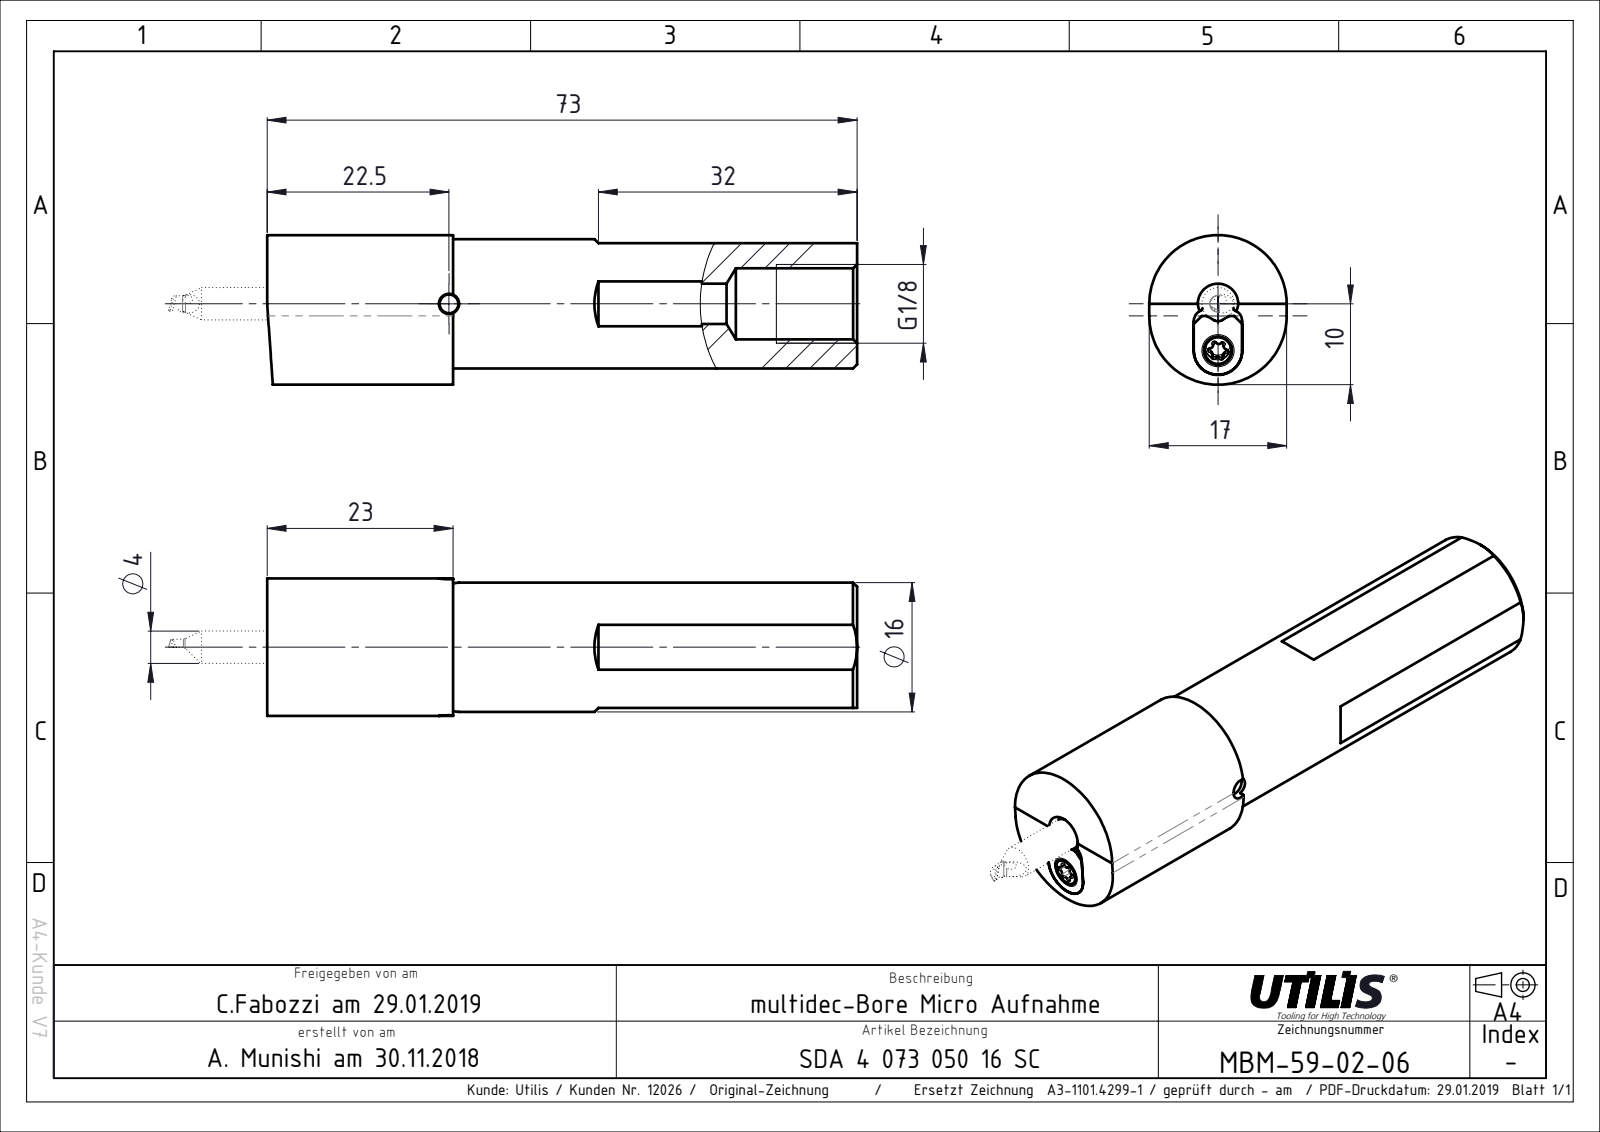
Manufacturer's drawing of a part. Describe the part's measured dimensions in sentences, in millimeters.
The part is named "MBM-59-02-06". Its 3-D file was written by "SolidWorks 2018 (CONFIG_CONTROL_DESIGN)". It is 1 solid with 49 faces: 15 planar, 18 cylindrical and 16 other. Overall it measures 73 by 18.5 by 17 millimeters. Its volume is 13 276 cubic millimeters and its surface area 5 800 square millimeters. Round holes: 1 of diameter 2.5, 1 of diameter 3.3, 1 of diameter 4, 1 of diameter 5, 1 of diameter 8.8. Round bosses or shafts: 1 of diameter 16. Partial cylindrical surfaces (rounded edges, fillets, slot ends): 2 of radius 8.5, 1 of radius 3. The main face-to-face distances are 73, 5.5, 11.5, 23, 50, 1, 16, 17, 10.5, 6.
